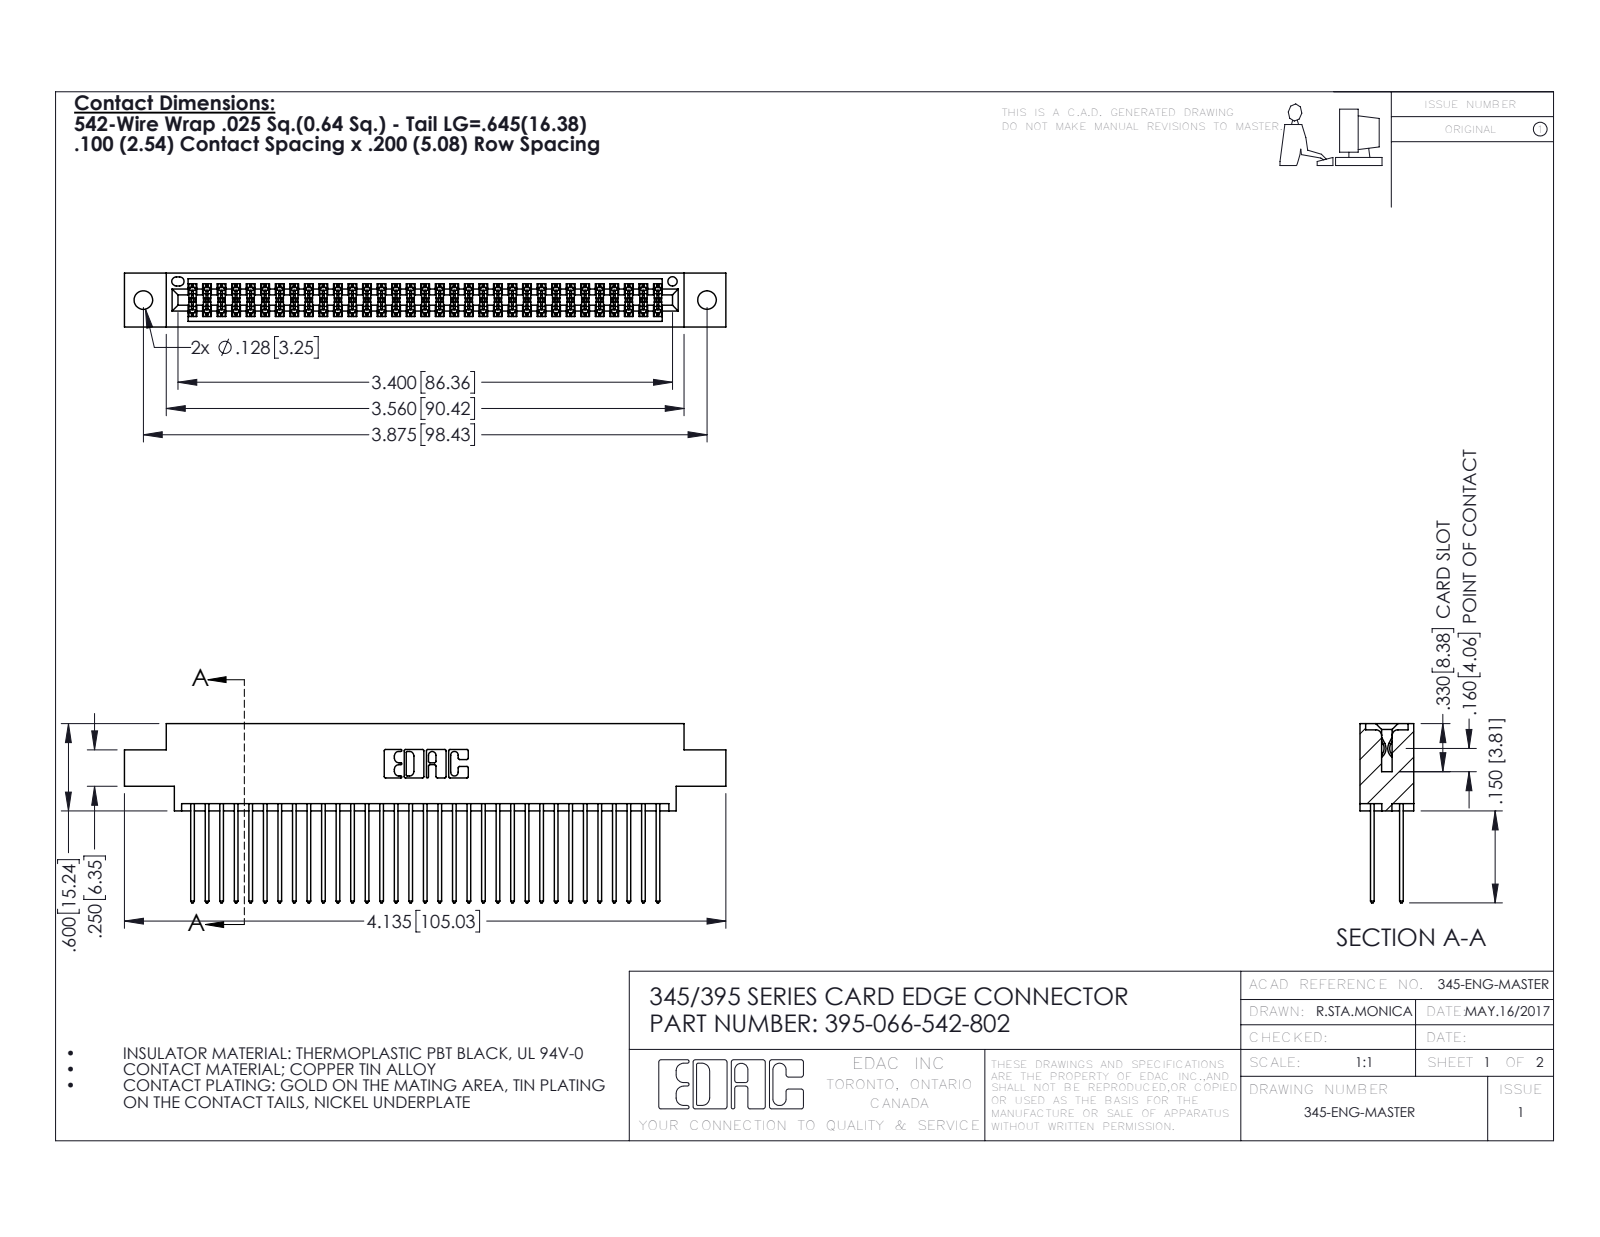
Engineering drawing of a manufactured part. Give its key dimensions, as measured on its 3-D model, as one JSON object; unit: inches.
{"part_name": "395-066-542-802; 345-292-001_345-293-142; 345 Part_0.170 Offset - 0.128 Dia", "step_written_by": "SolidWorks 2016 (CONFIG_CONTROL_DESIGN)", "units": "inches", "bodies": {"solids": 67, "faces": 3430, "planar": 2262, "cylindrical": 1168, "other": 0}, "overall_size": [4.135, 1.232, 0.37], "volume_in3": 0.627, "surface_area_in2": 25.3, "round_holes": [[0.128, 2], [0.064, 1]], "partial_cylinders_radius": [[0.006, 99], [0.01, 66], [0.01, 22], [0.007, 6], [0.031, 6], [0.026, 3], [0.014, 2], [0.019, 2]], "face_to_face_distances": [0.298, 0.072, 0.2, 0.098, 0.272, 0.025, 0.37, 0.225, 0.175, 0.149], "hole_center_spacings": [0.27, 3.64, 3.875]}
